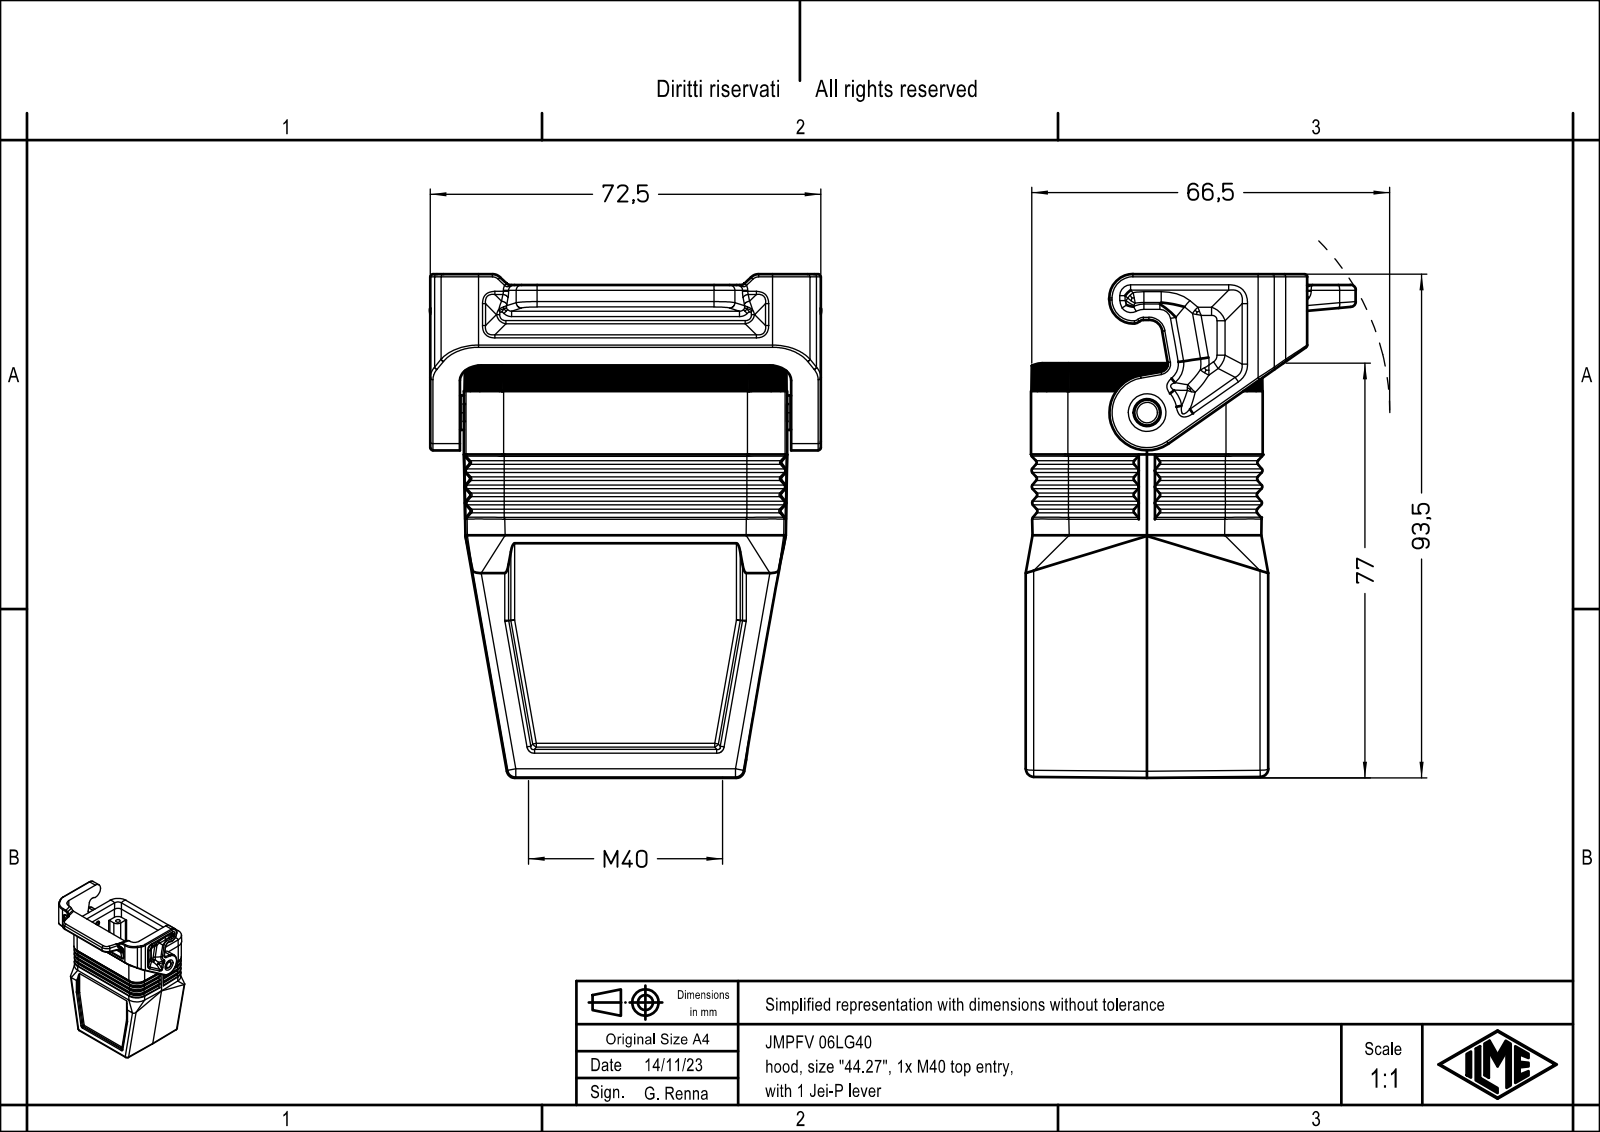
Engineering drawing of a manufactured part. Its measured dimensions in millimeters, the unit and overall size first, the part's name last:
Units: millimetres
Overall size (bounding box): 93.45 × 72.58 × 61.25
Round holes (diameter × count): ⌀38.6 ×1
Round bosses / shafts (diameter × count): ⌀6.4 ×1, ⌀4.8 ×1
Partial cylindrical surfaces — rounded edges, fillets, slot ends (radius × count): R0.5 ×92, R1 ×47, R3 ×24, R1.5 ×22, R0.33 ×15, R7 ×13, R2 ×12, R4 ×8
Main face-to-face distances: 43, 2, 1.02, 3.25, 46.25, 7, 1, 44, 61.5, 5.5
Volume: 76 844 mm³ · Surface area: 36 627 mm²
Bodies: 1 solid, 858 faces (254 planar, 282 cylindrical, 322 other)
Part name (STEP PRODUCT): JMPFV 06LG40
STEP written by: Creo Elements/Direct Modeling 20.1B 02-Apr-2019 (C) Parametric Technology GmbH (AUTOMOTIVE_DESIGN)
